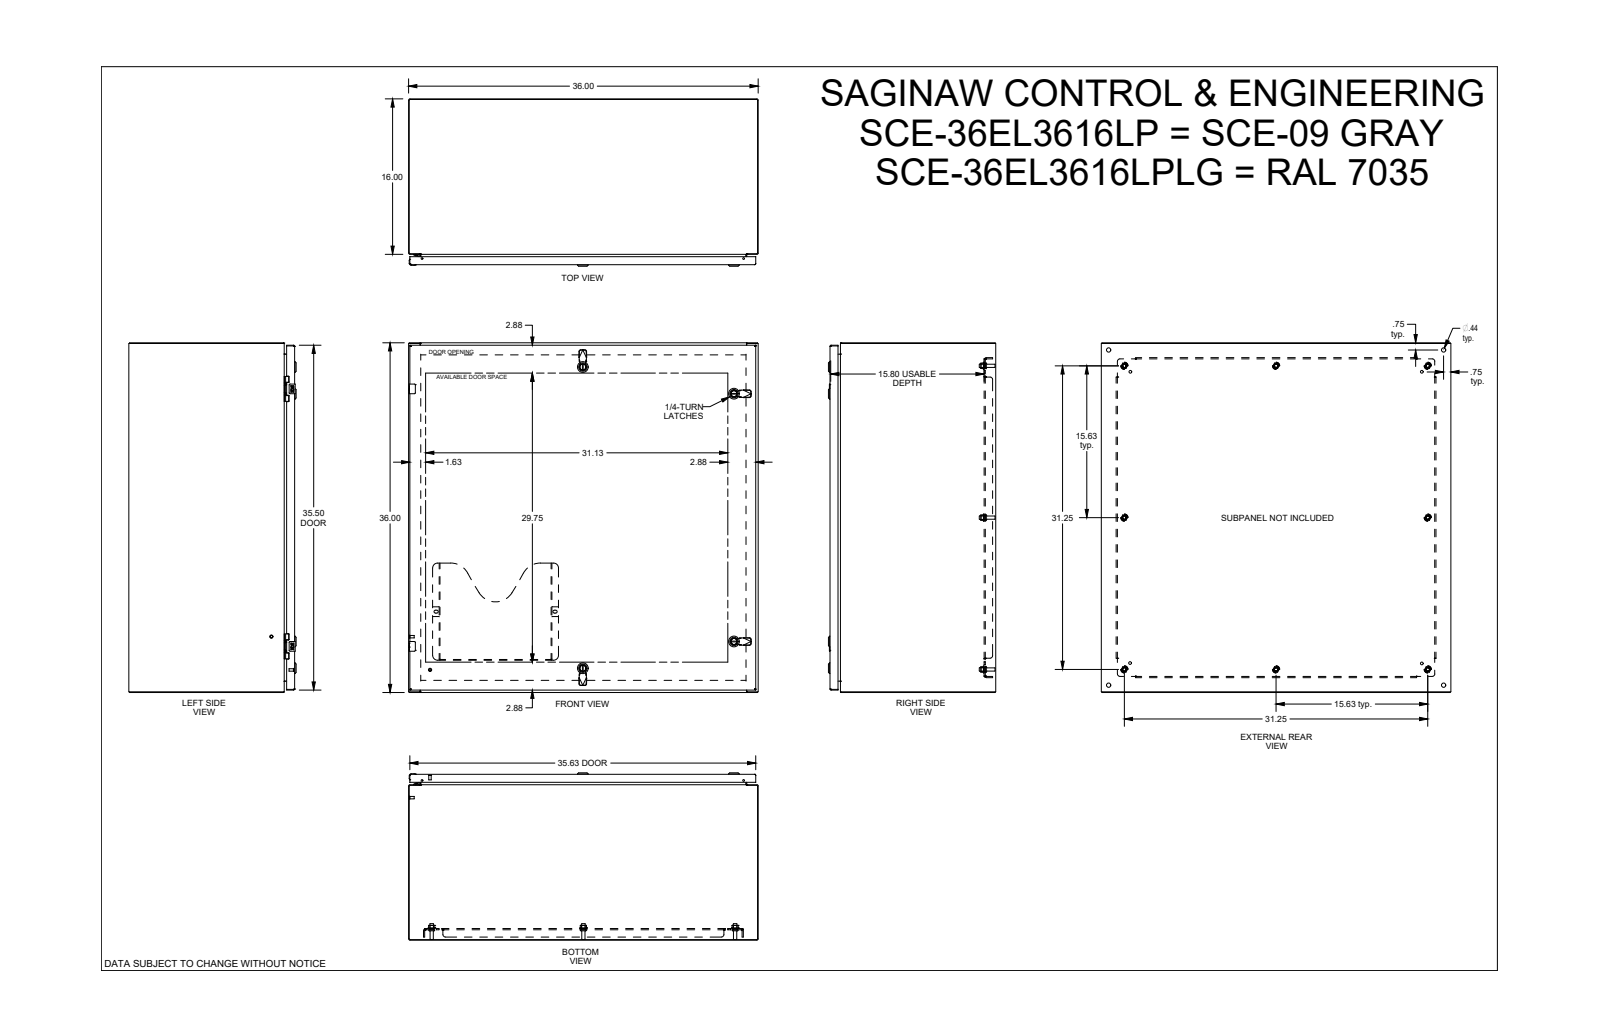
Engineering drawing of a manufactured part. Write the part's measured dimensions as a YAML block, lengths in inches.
part_name: "SCE-36EL3616LP"
step_written_by: "SolidWorks 2021 (AUTOMOTIVE_DESIGN)"
units: inches
bodies: {solids: 65, faces: 3426, planar: 1489, cylindrical: 991, other: 946}
overall_size: [36, 36, 17.23]
volume: 562.1
surface_area: 13480
round_holes:
  - {diameter: 0.367, count: 8}
  - {diameter: 0.5, count: 8}
  - {diameter: 0.172, count: 4}
  - {diameter: 0.197, count: 4}
  - {diameter: 0.205, count: 4}
  - {diameter: 0.244, count: 4}
  - {diameter: 0.266, count: 4}
  - {diameter: 0.281, count: 4}
  - {diameter: 0.315, count: 4}
  - {diameter: 0.375, count: 4}
  - {diameter: 0.394, count: 4}
  - {diameter: 0.437, count: 4}
round_bosses_or_shafts:
  - {diameter: 0.366, count: 8}
  - {diameter: 0.332, count: 8}
  - {diameter: 0.17, count: 6}
  - {diameter: 1.102, count: 4}
  - {diameter: 0.78, count: 4}
  - {diameter: 0.63, count: 4}
  - {diameter: 0.531, count: 4}
  - {diameter: 0.504, count: 4}
partial_cylinders:
  - {radius: 0.012, count: 110}
  - {radius: 0.01, count: 52}
  - {radius: 0.02, count: 44}
  - {radius: 0.015, count: 20}
  - {radius: 0.04, count: 17}
  - {radius: 0.157, count: 16}
  - {radius: 0.06, count: 13}
  - {radius: 0.029, count: 12}
face_to_face_distances: [0.075, 35.925, 0.075, 0.06, 17.073, 16.998, 17.013, 16.938, 1.2, 15.873]
hole_center_spacings: [17.326, 37.126, 0.985, 15.019, 26.5, 32.334, 34.11, 0.02]
